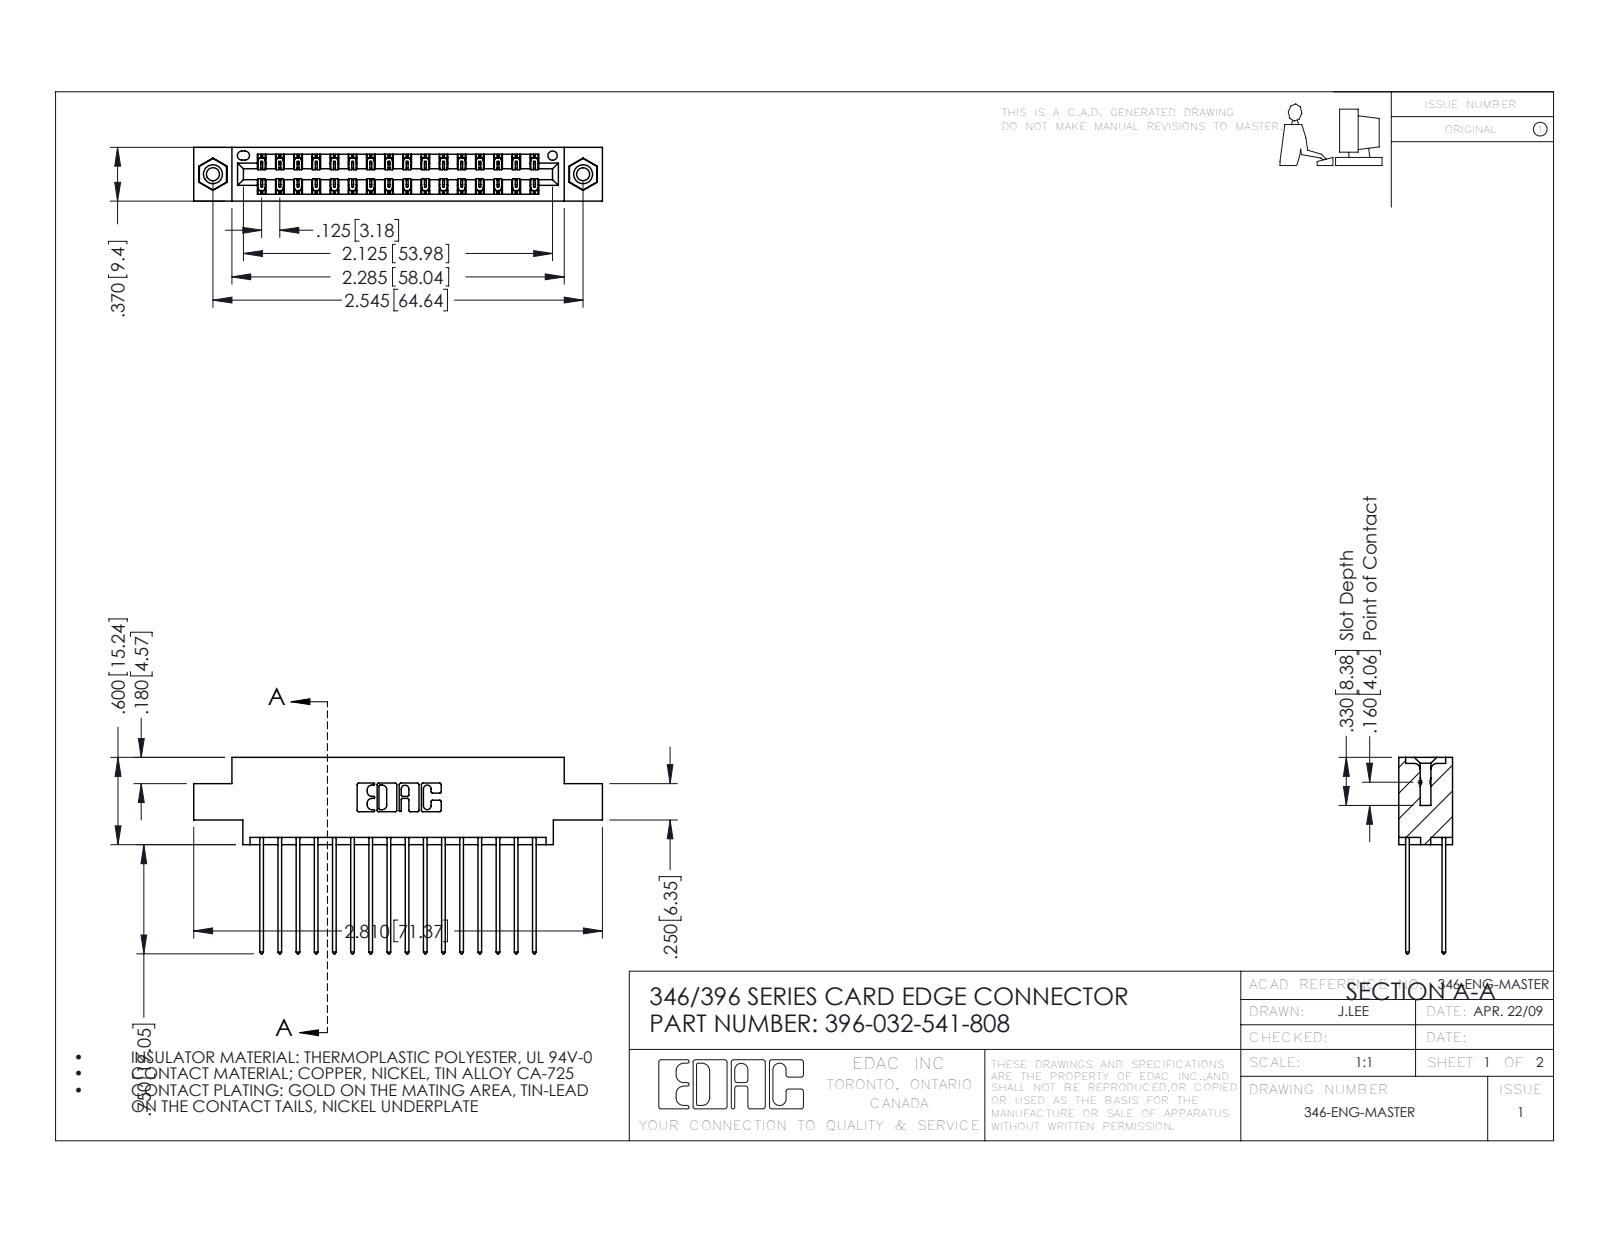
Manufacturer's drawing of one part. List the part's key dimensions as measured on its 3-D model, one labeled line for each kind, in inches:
Part name (STEP PRODUCT): 345-292-001_345-293-141; 346 Part_0.170 Offset - 0.156 Dia-TI; 396-032-541-808; 345-250-001_345-250-003-102
STEP written by: SolidWorks 2016 (CONFIG_CONTROL_DESIGN)
Units: inches
Bodies: 35 solids, 1850 faces (1232 planar, 602 cylindrical, 16 other)
Overall size (bounding box): 2.81 × 1.35 × 0.37
Volume: 0.414 in³ · Surface area: 15.49 in²
Round holes (diameter × count): ⌀0.089 ×2, ⌀0.125 ×2, ⌀0.156 ×2, ⌀0.064 ×1
Round bosses / shafts (diameter × count): ⌀0.155 ×2
Partial cylindrical surfaces — rounded edges, fillets, slot ends (radius × count): R0.006 ×48, R0.01 ×32, R0.01 ×22, R0.007 ×6, R0.031 ×6, R0.026 ×3, R0.014 ×2, R0.022 ×2
Main face-to-face distances: 0.048, 0.322, 0.25, 0.37, 0.072, 0.298, 0.025, 0.275, 0.222, 0.148
Hole centre spacings: 0.246, 2.338, 2.545
